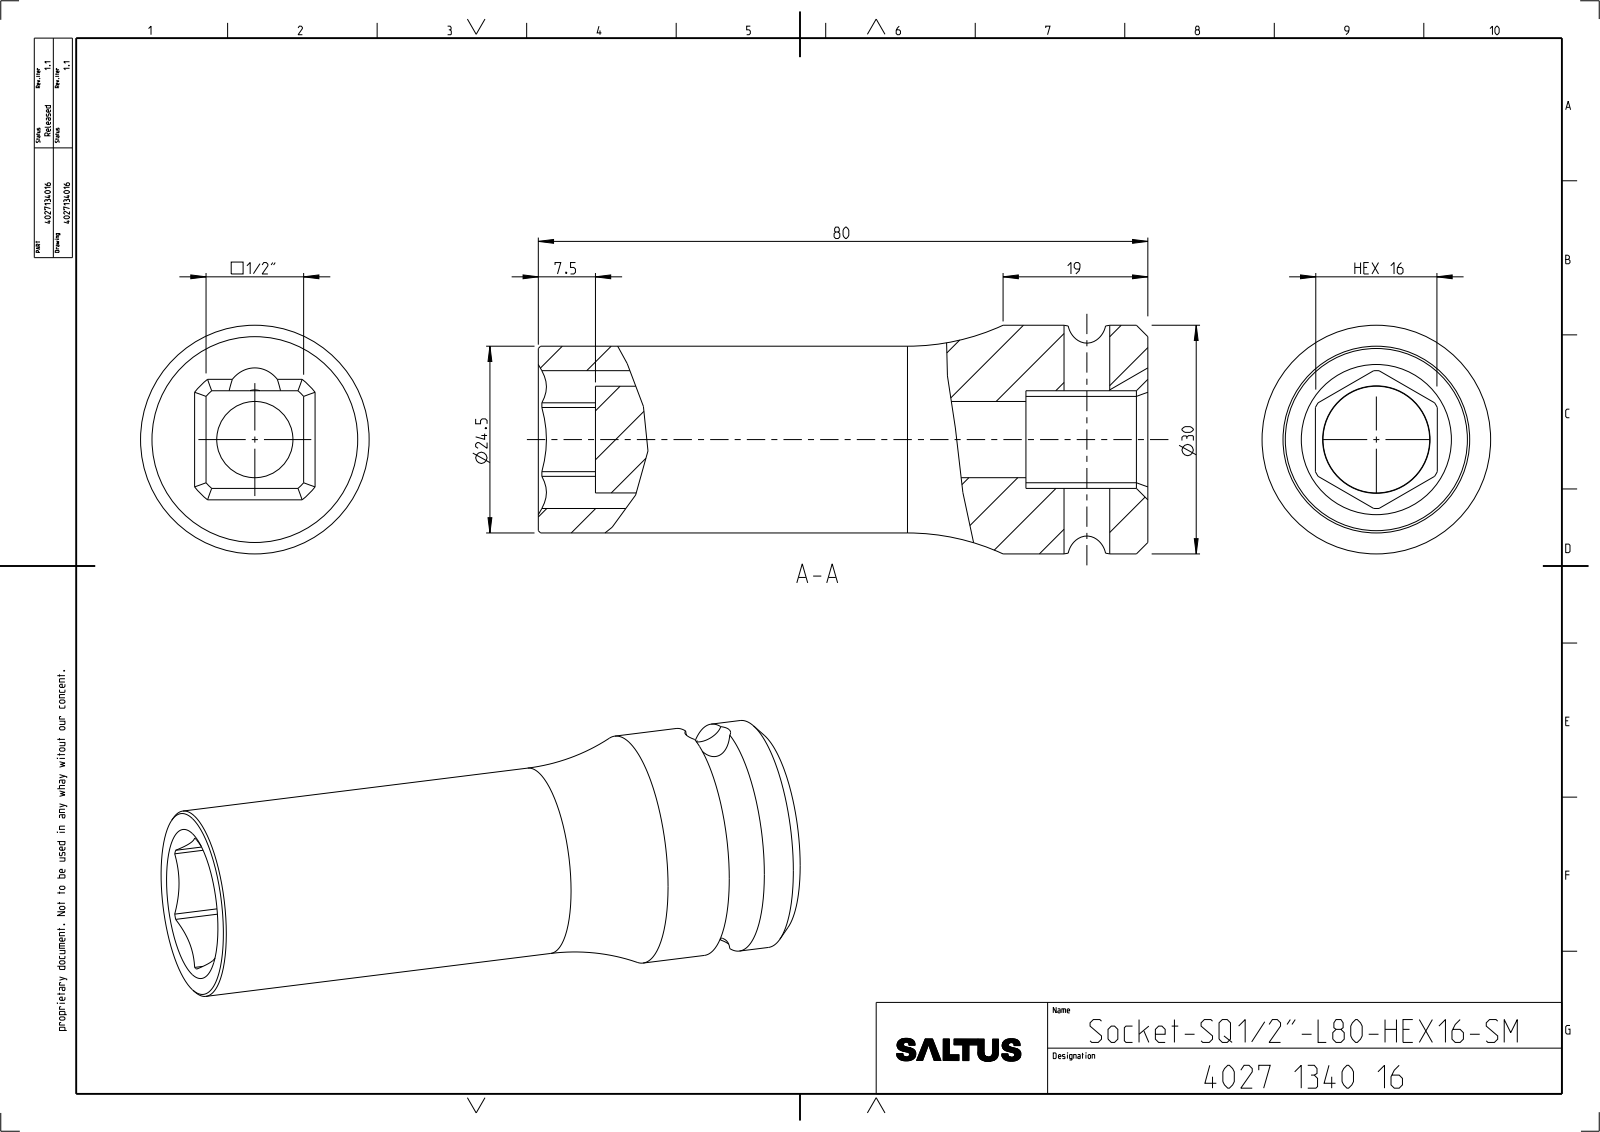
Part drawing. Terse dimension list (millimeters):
name: 4027134016
written by: CREO PARAMETRIC BY PTC INC, 2022414 (CONFIG_CONTROL_DESIGN)
unit: mm
bodies: 2 solids, 63 faces (22 planar, 27 cylindrical, 14 other)
size: 80 × 30 × 30
volume: 31 202 mm³; area: 12 136 mm²
holes: 1× ⌀6, 1× ⌀10, 1× ⌀14.1
bosses: 1× ⌀30, 1× ⌀24.5, 1× ⌀14
rounds: 1× R4, 1× R8.55, 1× R9.04
face distances: 16, 12.82, 1.59, 14.41, 60.82, 72.5, 11.68, 80, 19.18, 7.5
